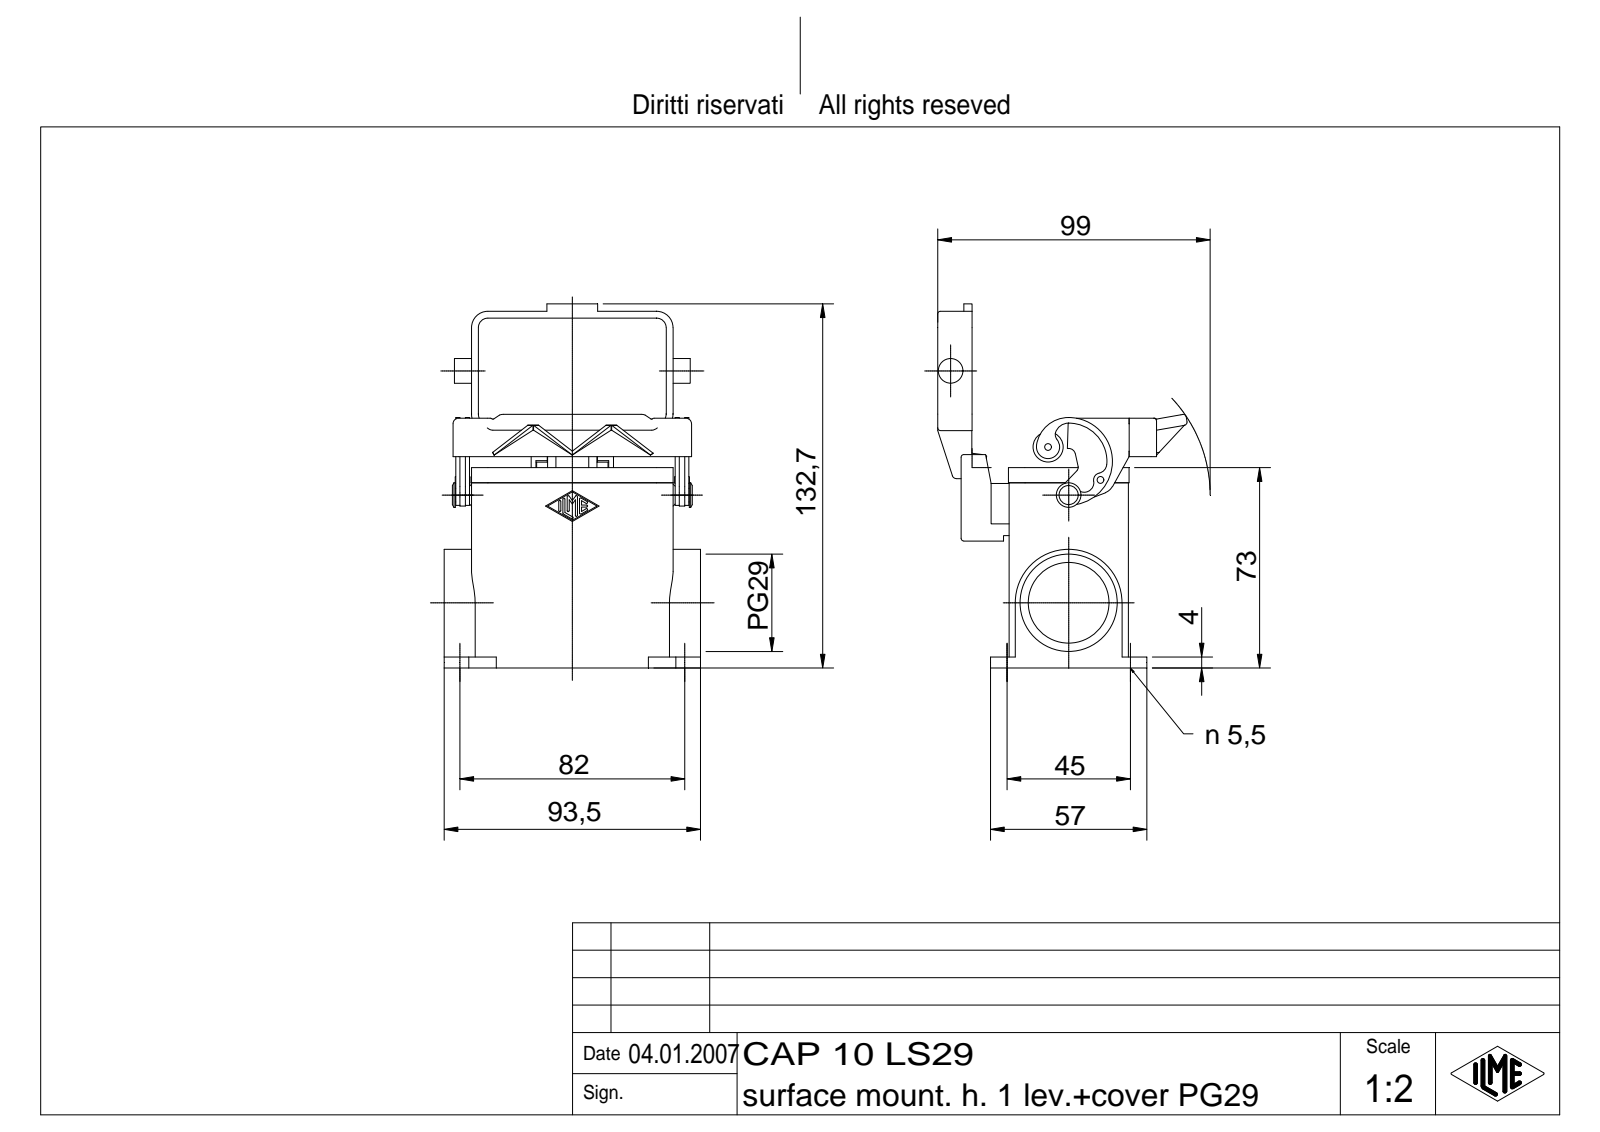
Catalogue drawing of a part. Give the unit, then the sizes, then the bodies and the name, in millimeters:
Units: millimetres
Overall size (bounding box): 132.7 × 93.5 × 90.95
Round holes (diameter × count): ⌀5.5 ×4, ⌀2 ×1, ⌀4 ×1, ⌀29.48 ×1, ⌀35.48 ×1
Round bosses / shafts (diameter × count): ⌀9 ×2, ⌀5 ×2, ⌀11 ×1, ⌀7 ×1, ⌀4 ×1, ⌀3 ×1, ⌀2.5 ×1
Partial cylindrical surfaces — rounded edges, fillets, slot ends (radius × count): R1 ×18, R0.38 ×14, R2 ×12, R6 ×12, R1.5 ×6, R3.5 ×6, R3 ×4, R0.5 ×3
Main face-to-face distances: 3, 40.5, 4, 43.5, 26, 37.5, 66.5, 69.5, 29, 66
Hole centre spacings: 45, 82, 93.54, 46.24
Volume: 125 940 mm³ · Surface area: 72 118 mm²
Bodies: 6 solids, 592 faces (252 planar, 180 cylindrical, 160 other)
Part name (STEP PRODUCT): CAP 10 LS29
STEP written by: Autodesk Inventor 7 (AUTOMOTIVE_DESIGN)
